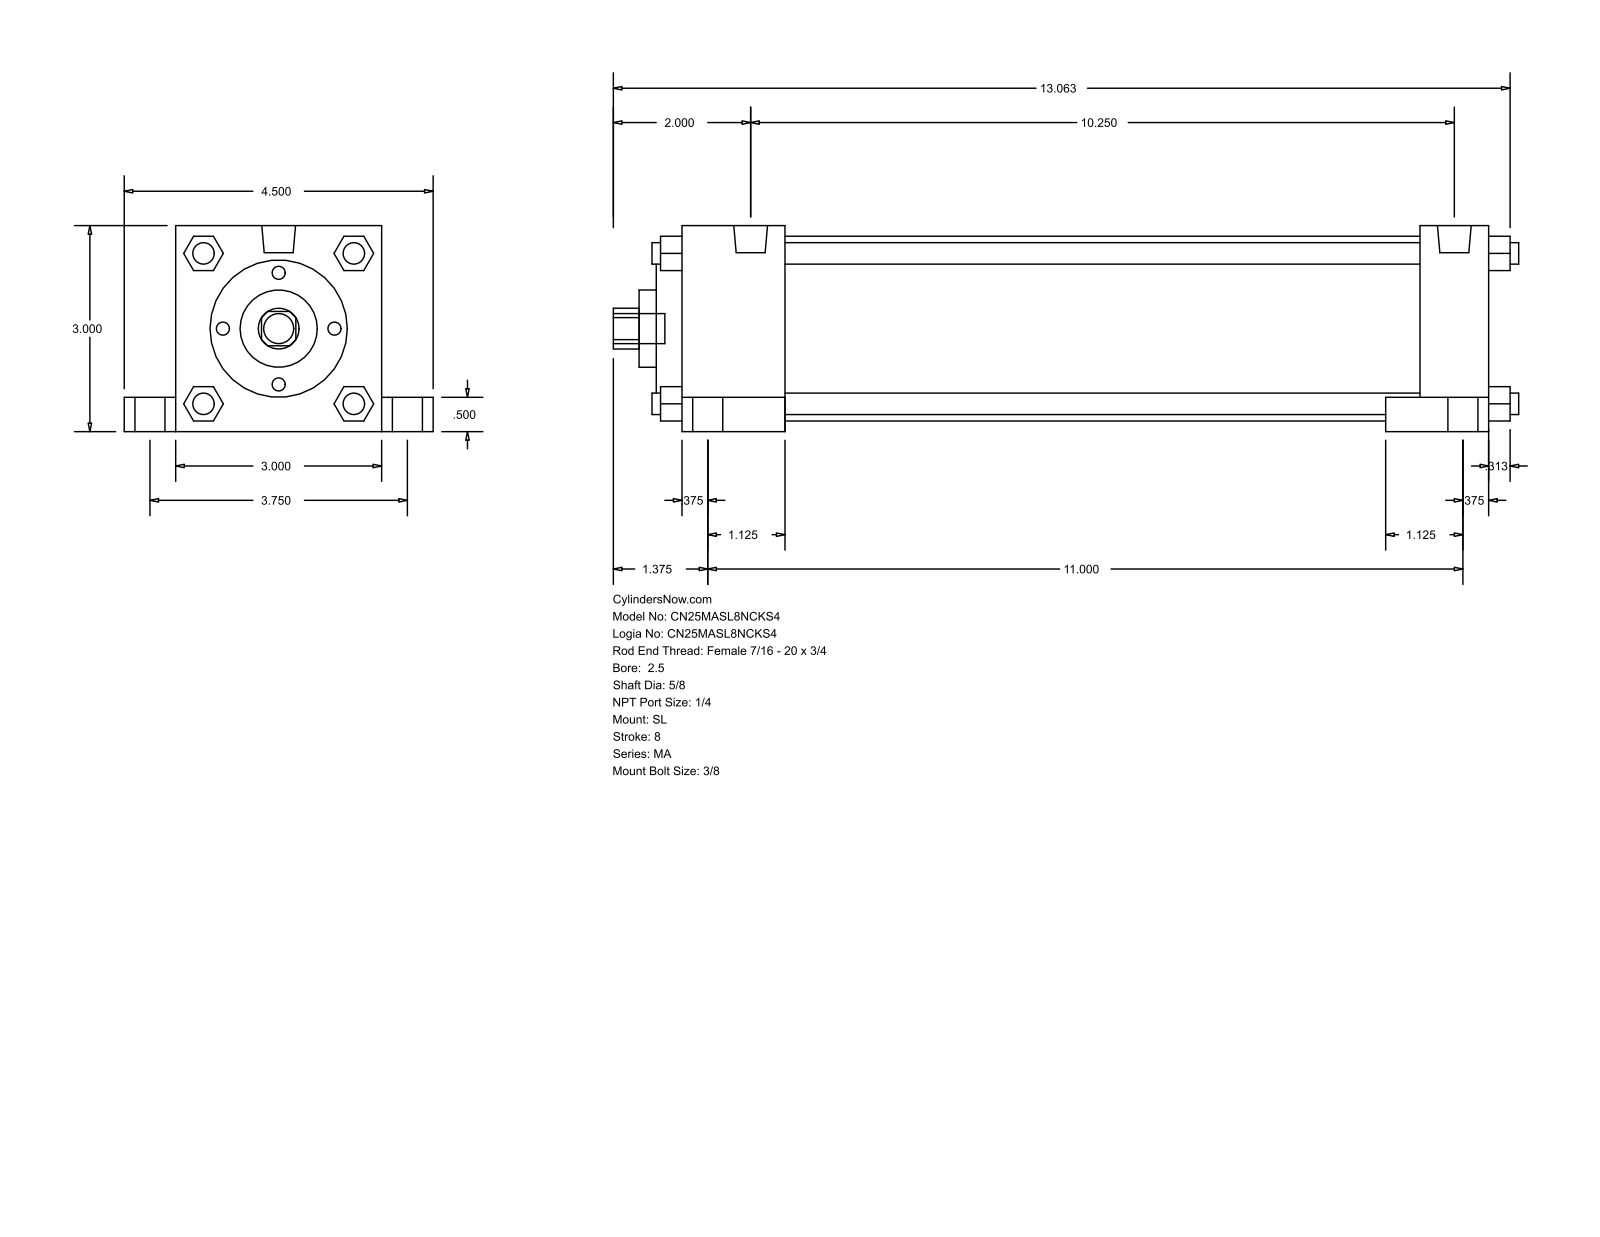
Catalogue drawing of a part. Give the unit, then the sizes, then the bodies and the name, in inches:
Units: inches
Overall size (bounding box): 13.187 × 4.5 × 3
Round holes (diameter × count): ⌀0.625 ×1, ⌀1.125 ×1, ⌀2 ×1, ⌀2.69 ×1
Round bosses / shafts (diameter × count): ⌀0.313 ×8, ⌀0.437 ×5, ⌀0.687 ×4, ⌀0.492 ×2
Partial cylindrical surfaces — rounded edges, fillets, slot ends (radius × count): R0.297 ×1
Main face-to-face distances: 3, 11.75, 0.5, 9.25, 1, 1.5, 10.25, 10.75, 0.75, 2.5
Bodies: 0 solids, 150 faces (113 planar, 37 cylindrical, 0 other)
Part name (STEP PRODUCT): MA_SL__0250_0.625
STEP written by: GSSL Pune (CONFIG_CONTROL_DESIGN)
